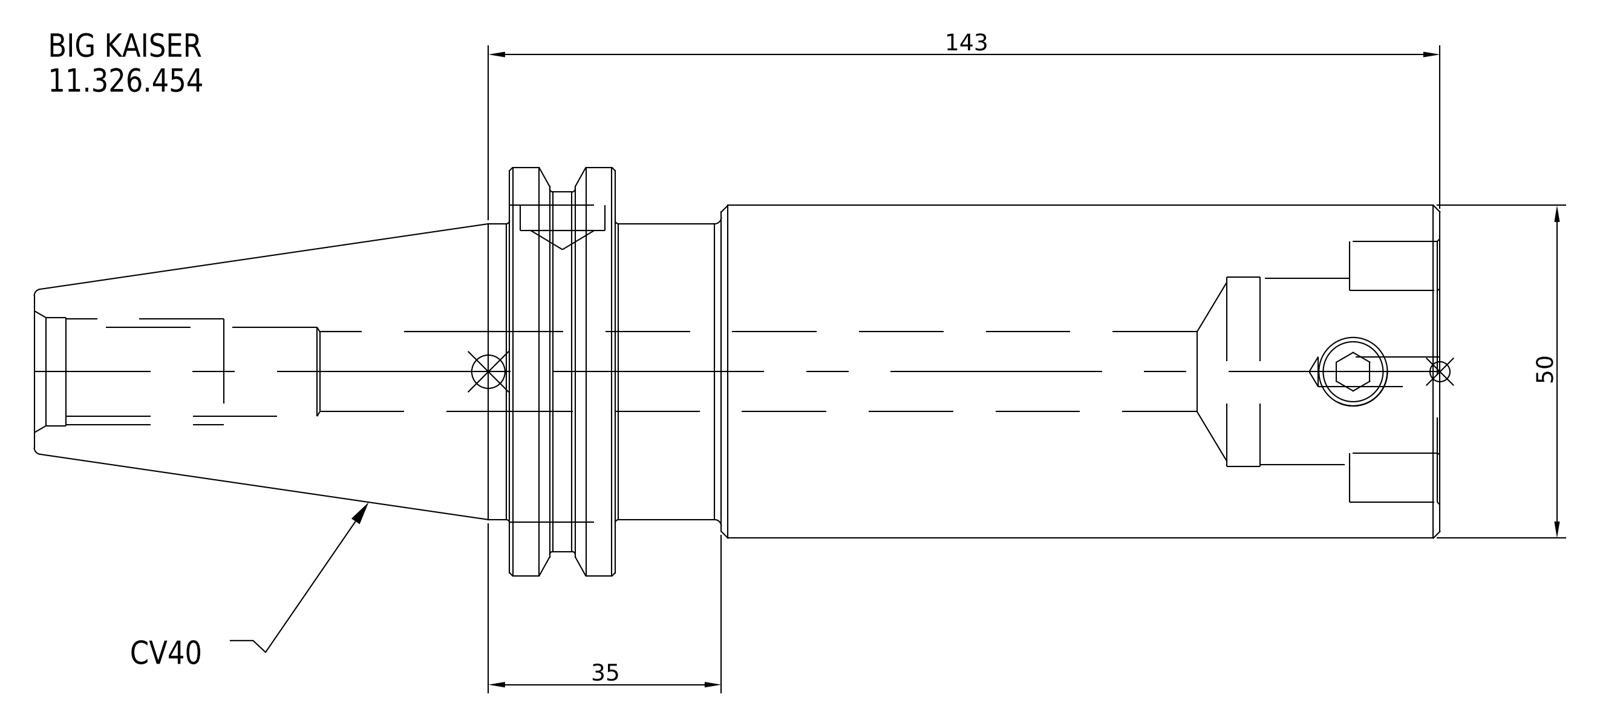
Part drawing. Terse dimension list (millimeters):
name: 11_326_454
written by: SolidWorks 2021 (CONFIG_CONTROL_DESIGN)
unit: mm
bodies: 2 solids, 17 faces (8 planar, 6 cylindrical, 3 other)
size: 211.25 × 63.5 × 63.5
volume: 354 103 mm³; area: 40 242 mm²
bosses: 1× ⌀63.5, 1× ⌀56.36, 1× ⌀50, 1× ⌀44.45
face distances: 107.95, 139.83, 31.88, 123.95, 16, 15.88, 211.25, 103.3, 87.3, 71.42
